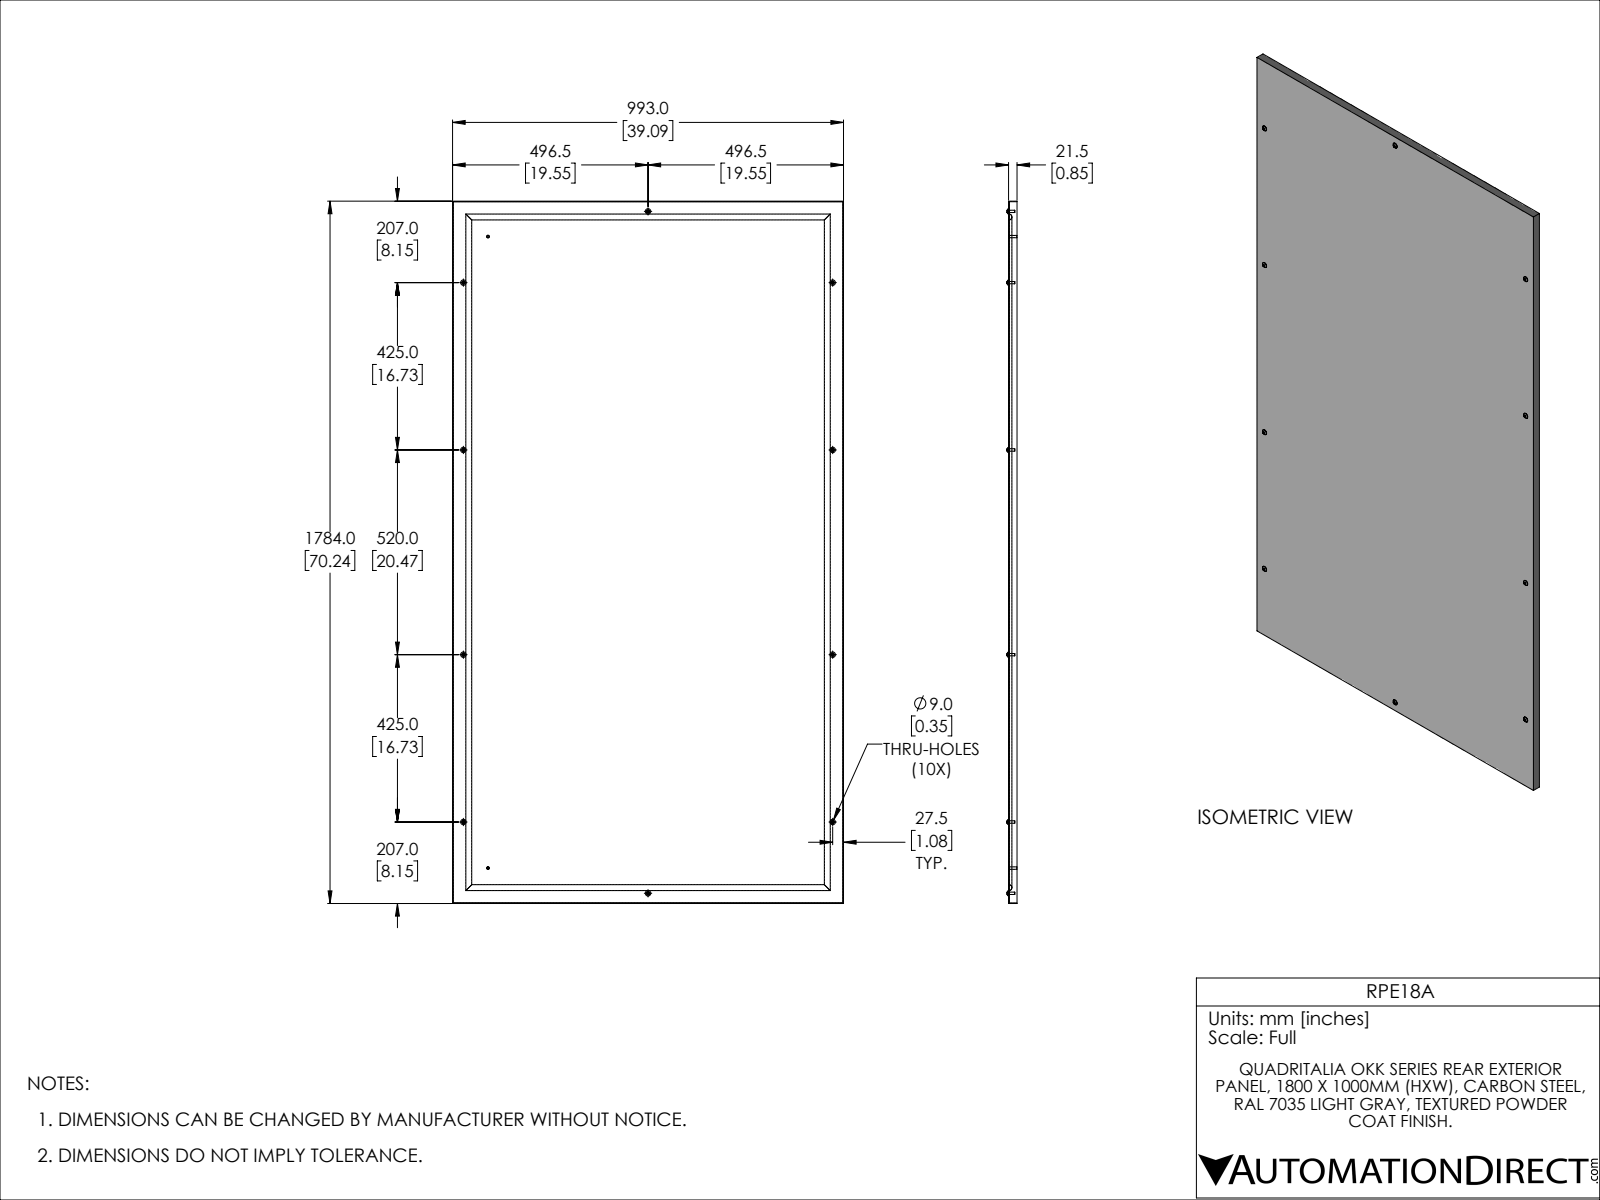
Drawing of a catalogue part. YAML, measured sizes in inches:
part_name: "RPE18A"
step_written_by: "SolidWorks 2021 (CONFIG_CONTROL_DESIGN)"
units: inches
bodies: {solids: 17, faces: 383, planar: 189, cylindrical: 162, other: 32}
overall_size: [70.236, 39.094, 0.992]
volume: 198.6
surface_area: 6166
round_holes:
  - {diameter: 0.354, count: 10}
round_bosses_or_shafts:
  - {diameter: 0.236, count: 12}
  - {diameter: 0.551, count: 10}
  - {diameter: 0.276, count: 2}
partial_cylinders:
  - {radius: 0.02, count: 120}
  - {radius: 0.296, count: 4}
face_to_face_distances: [0.059, 39.035, 70.177, 39.094, 38.976, 70.236, 70.118, 0.846, 0.787, 22.073]
hole_center_spacings: [16.732, 19.792, 30.169, 36.929, 37.205, 40.543, 48.022, 52.421]
